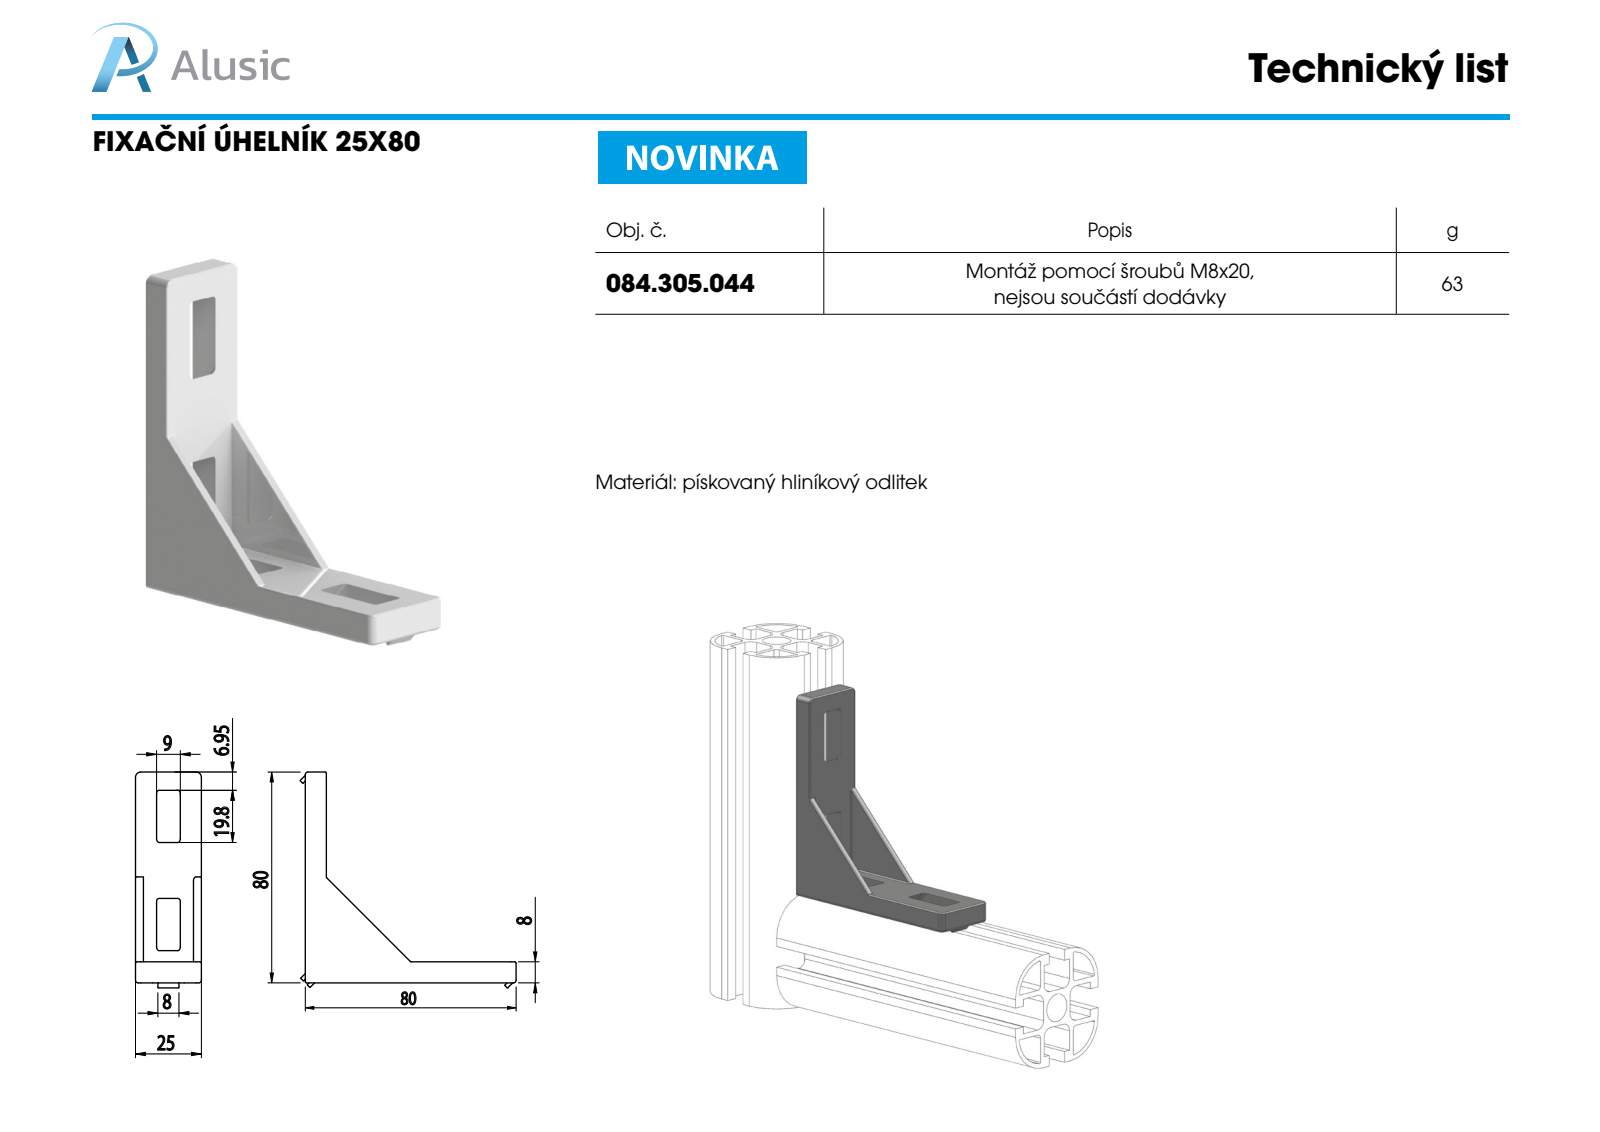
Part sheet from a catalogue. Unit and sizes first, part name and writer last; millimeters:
Units: millimetres
Overall size (bounding box): 81.9 × 81.9 × 25
Round bosses / shafts (diameter × count): ⌀4 ×2
Partial cylindrical surfaces — rounded edges, fillets, slot ends (radius × count): R0.5 ×67, R0.2 ×44, R1 ×23, R2 ×4
Main face-to-face distances: 8, 2.5, 5.5, 17, 22.5, 25, 14.5, 20, 3, 9
Volume: 23 110 mm³ · Surface area: 14 364 mm²
Bodies: 1 solid, 344 faces (81 planar, 162 cylindrical, 101 other)
Part name (STEP PRODUCT): 084.305.044
STEP written by: SolidWorks 2018 (AUTOMOTIVE_DESIGN)
